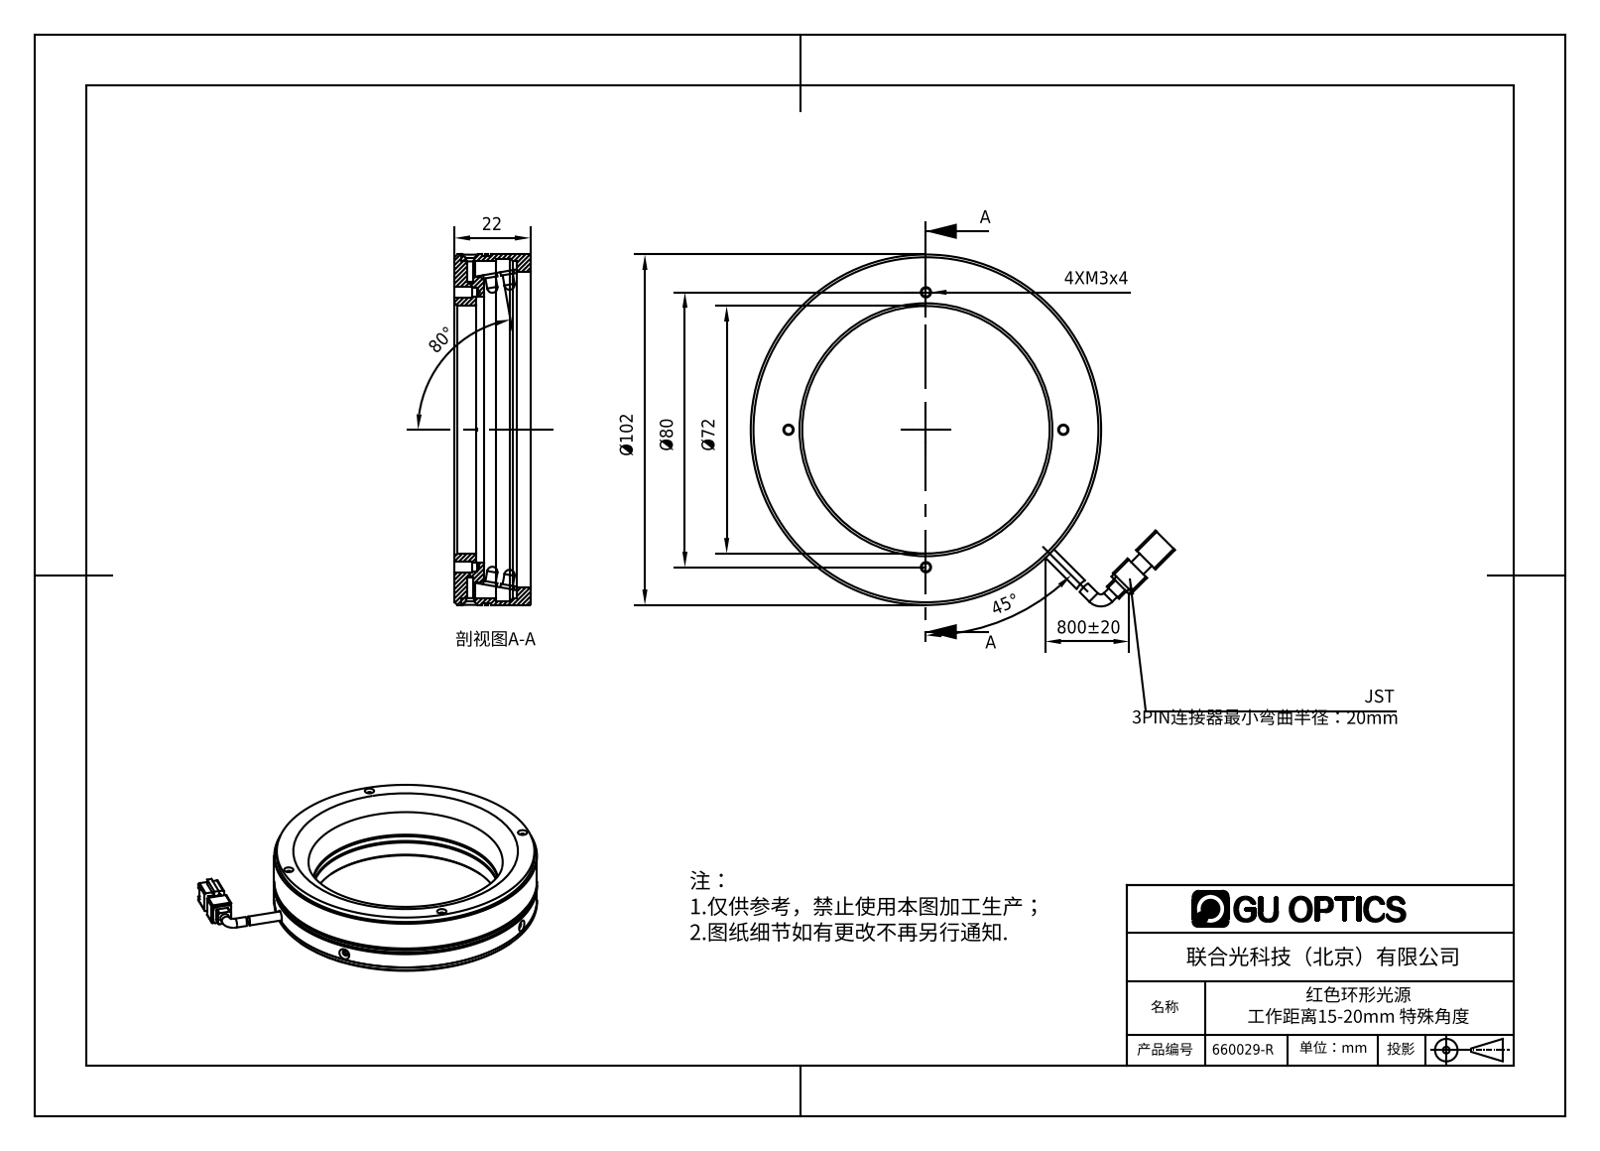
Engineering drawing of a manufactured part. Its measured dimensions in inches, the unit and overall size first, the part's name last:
Units: inches
Overall size (bounding box): 4.861 × 4.032 × 0.957
Round holes (diameter × count): ⌀0.049 ×4, ⌀0.067 ×4, ⌀0.098 ×4, ⌀0.118 ×4, ⌀0.063 ×2, ⌀0.094 ×2, ⌀0.138 ×2, ⌀2.835 ×1, ⌀3.055 ×1, ⌀3.622 ×1, ⌀3.858 ×1, ⌀3.921 ×1
Round bosses / shafts (diameter × count): ⌀0.15 ×105, ⌀0.118 ×105, ⌀0.138 ×2, ⌀4.016 ×1, ⌀3.976 ×1, ⌀3.937 ×1, ⌀3.508 ×1, ⌀2.992 ×1
Partial cylindrical surfaces — rounded edges, fillets, slot ends (radius × count): R0.02 ×8, R0.039 ×4, R0.063 ×1, R0.276 ×1
Main face-to-face distances: 0.866, 0.079, 0.236, 0.157, 0.63, 0.709, 0.945, 0.098, 0.472, 0.039
Hole centre spacings: 1.346, 3.185, 1.575, 1.87, 2.227, 2.645, 3.15, 3.741
Volume: 3.63 in³ · Surface area: 93.35 in²
Bodies: 111 solids, 2068 faces (1343 planar, 545 cylindrical, 180 other)
Part name (STEP PRODUCT): 660029-R
STEP written by: SolidWorks 2016 (AUTOMOTIVE_DESIGN)
